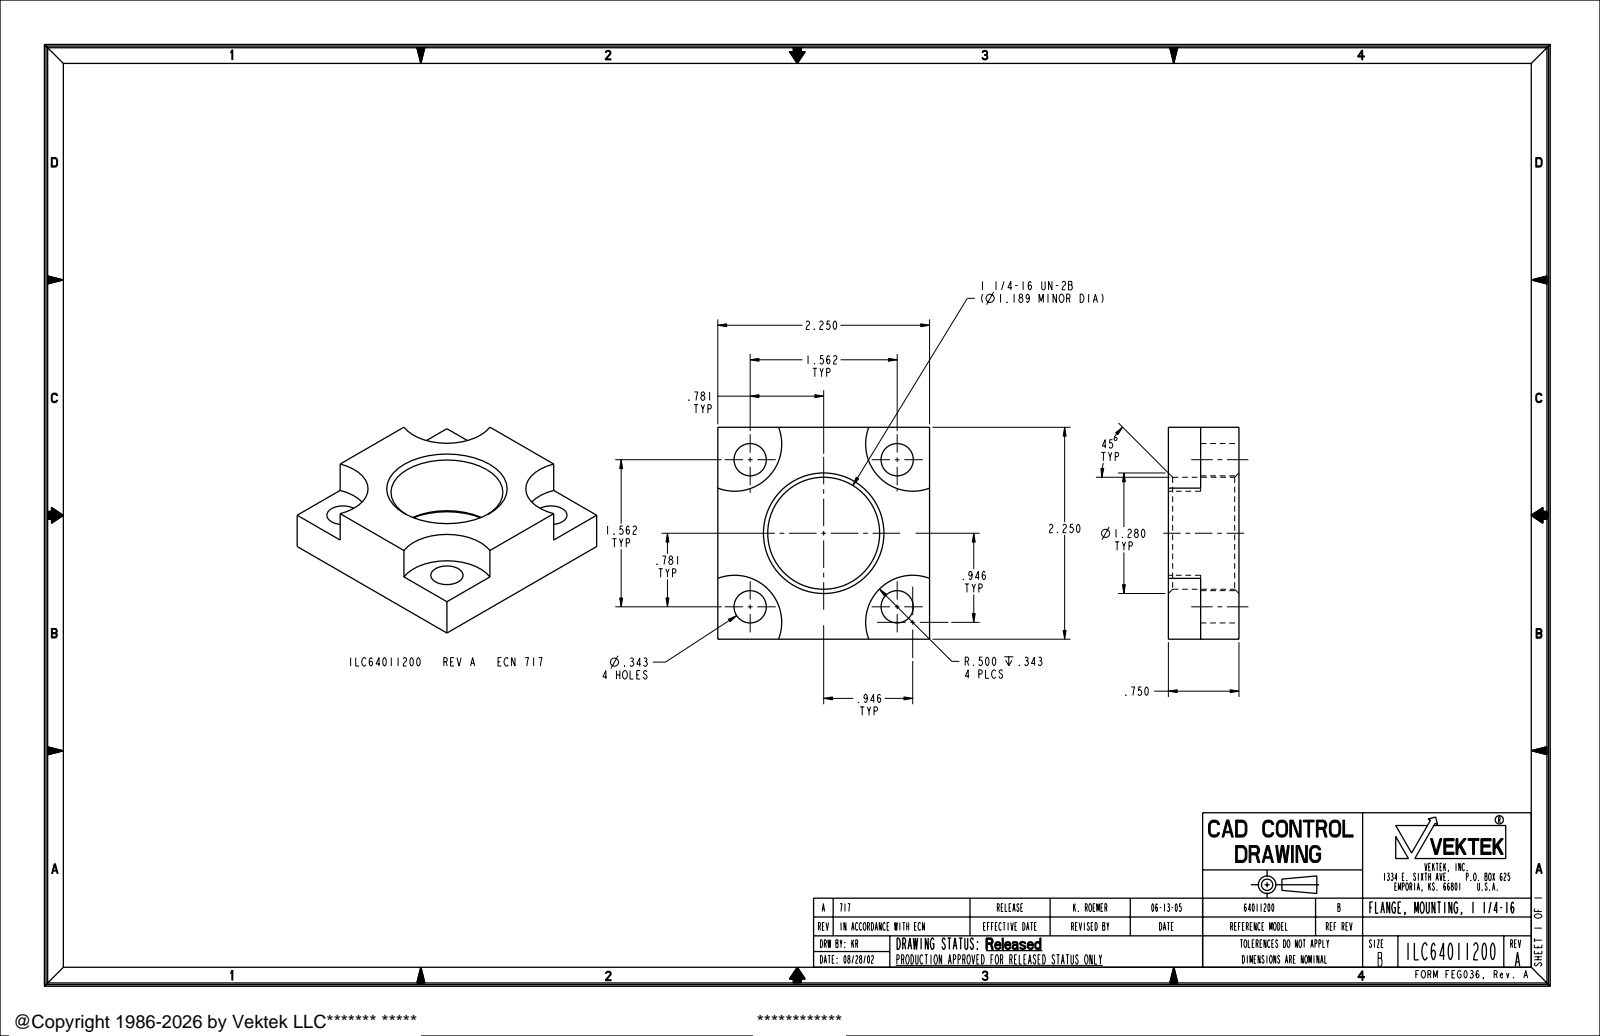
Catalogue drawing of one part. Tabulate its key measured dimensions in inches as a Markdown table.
| quantity | value |
| --- | --- |
| part name | ILC64011200 |
| STEP written by | PRO/ENGINEER BY PARAMETRIC TECHNOLOGY CORPORATION, 2004290 (AUTOMOTIVE_DESIGN_CC2) |
| units | inches |
| bodies | 1 solid, 28 faces (10 planar, 14 cylindrical, 4 other) |
| overall size | 2.25 × 2.25 × 0.75 |
| volume | 2.252 in³ |
| surface area | 18.08 in² |
| round holes (diameter × count) | 0.343 × 4, 1.189 × 1 |
| partial cylindrical surfaces (radius × count) | 0.5 × 4 |
| main face-to-face distances | 2.25, 0.75, 0.407, 0.343 |
| hole center spacings | 1.105, 1.562, 2.209 |
